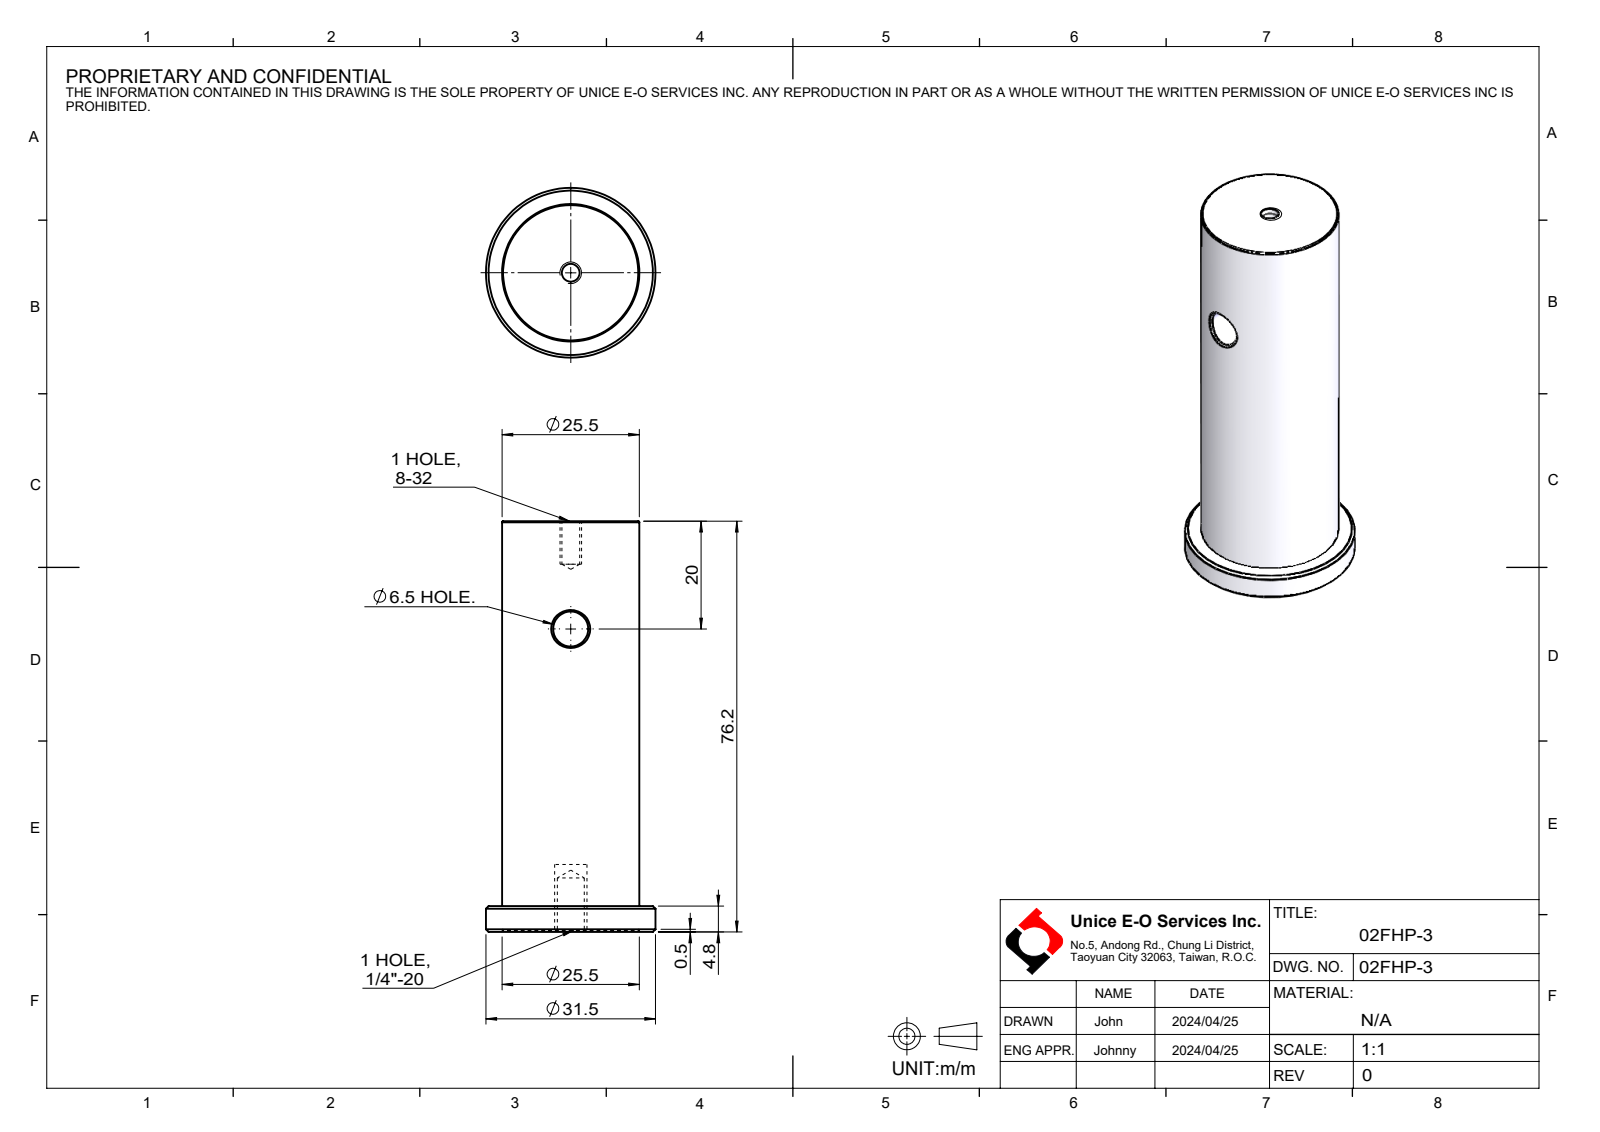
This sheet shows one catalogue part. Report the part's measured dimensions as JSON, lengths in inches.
{"part_name": "02FHP-3", "step_written_by": "SolidWorks 2021 (CONFIG_CONTROL_DESIGN)", "units": "inches", "bodies": {"solids": 1, "faces": 34, "planar": 4, "cylindrical": 12, "other": 18}, "overall_size": [3, 1.24, 1.24], "volume_in3": 2.369, "surface_area_in2": 13, "round_holes": [[0.13, 1], [0.197, 1], [0.256, 1], [1.004, 1]], "round_bosses_or_shafts": [[1.24, 1]], "face_to_face_distances": [2.98, 0.169, 2.811, 0.02, 0.189, 3]}
